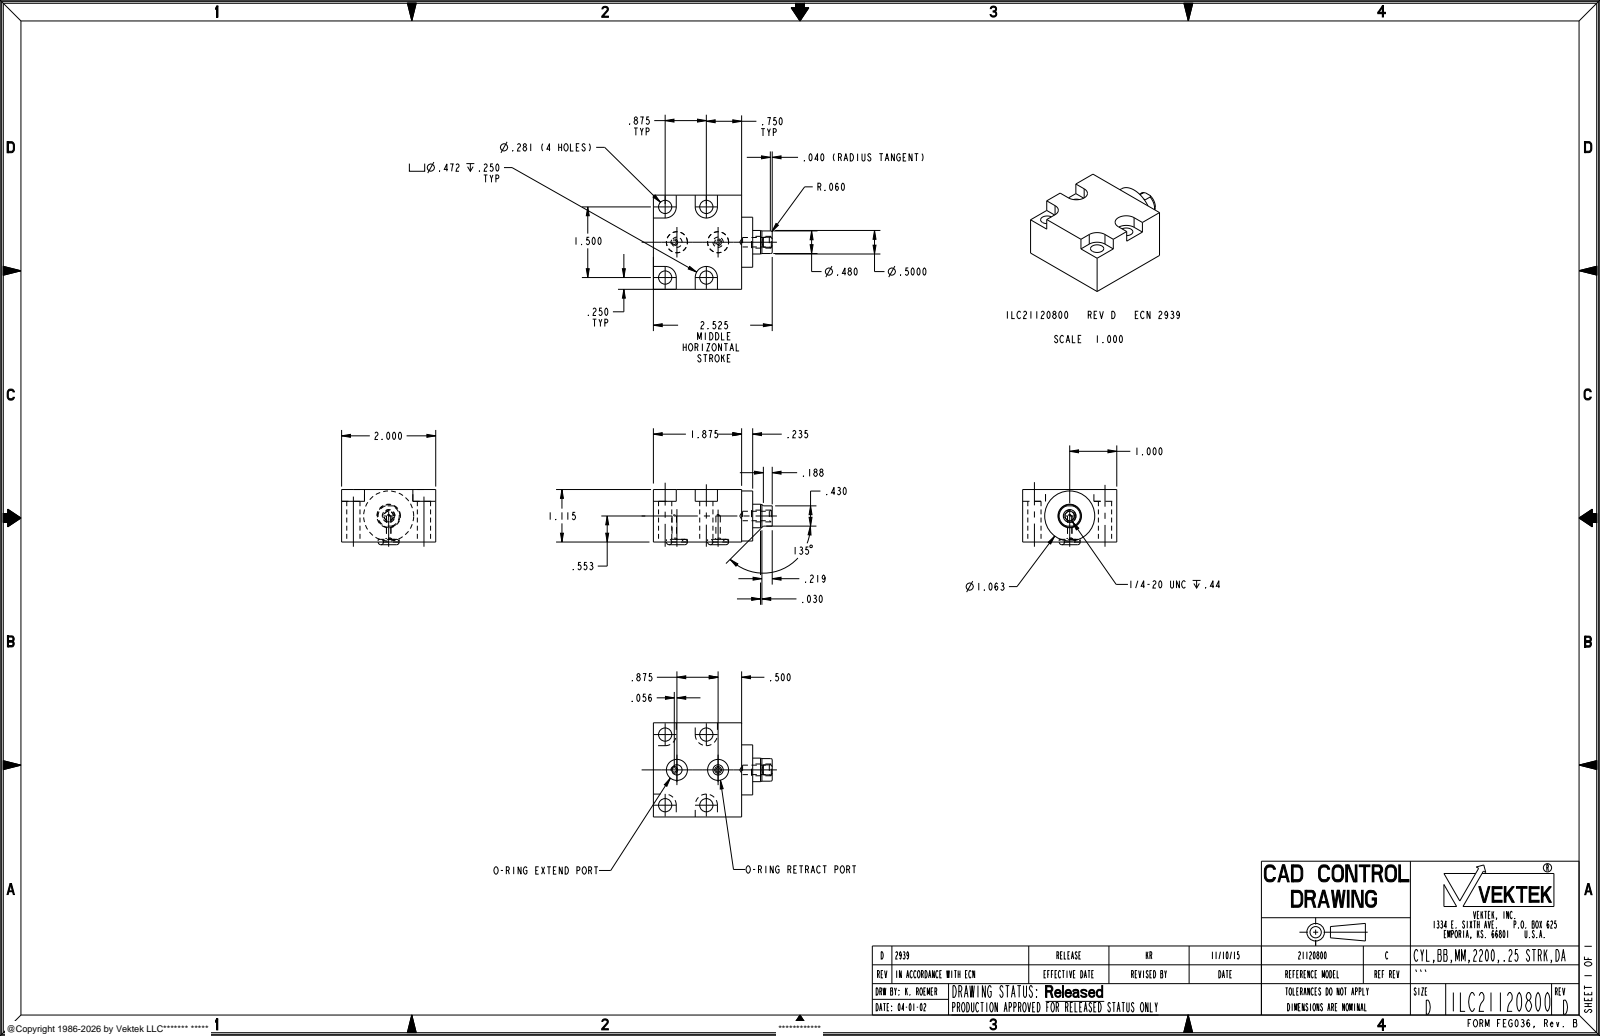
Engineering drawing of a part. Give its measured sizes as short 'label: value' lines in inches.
name: ILC21120800
written by: PRO/ENGINEER BY PARAMETRIC TECHNOLOGY CORPORATION, 2013320 (AUTOMOTIVE_DESIGN)
unit: in
bodies: 1 solid, 81 faces (27 planar, 30 cylindrical, 24 other)
size: 2.525 × 2 × 1.172
volume: 4.011 in³; area: 22.36 in²
holes: 4× ⌀0.281, 2× ⌀0.094, 2× ⌀0.447, 1× ⌀0.201
bosses: 1× ⌀1.063, 1× ⌀0.5, 1× ⌀0.48, 1× ⌀0.25
rounds: 4× R0.236
face distances: 1.115, 2, 1.875, 0.235, 2.11, 0.865, 0.25, 0.057, 0.808, 1.058
hole spacings: 0.791, 0.875, 0.775, 0.976, 1.013, 1.352, 1.5, 1.737
